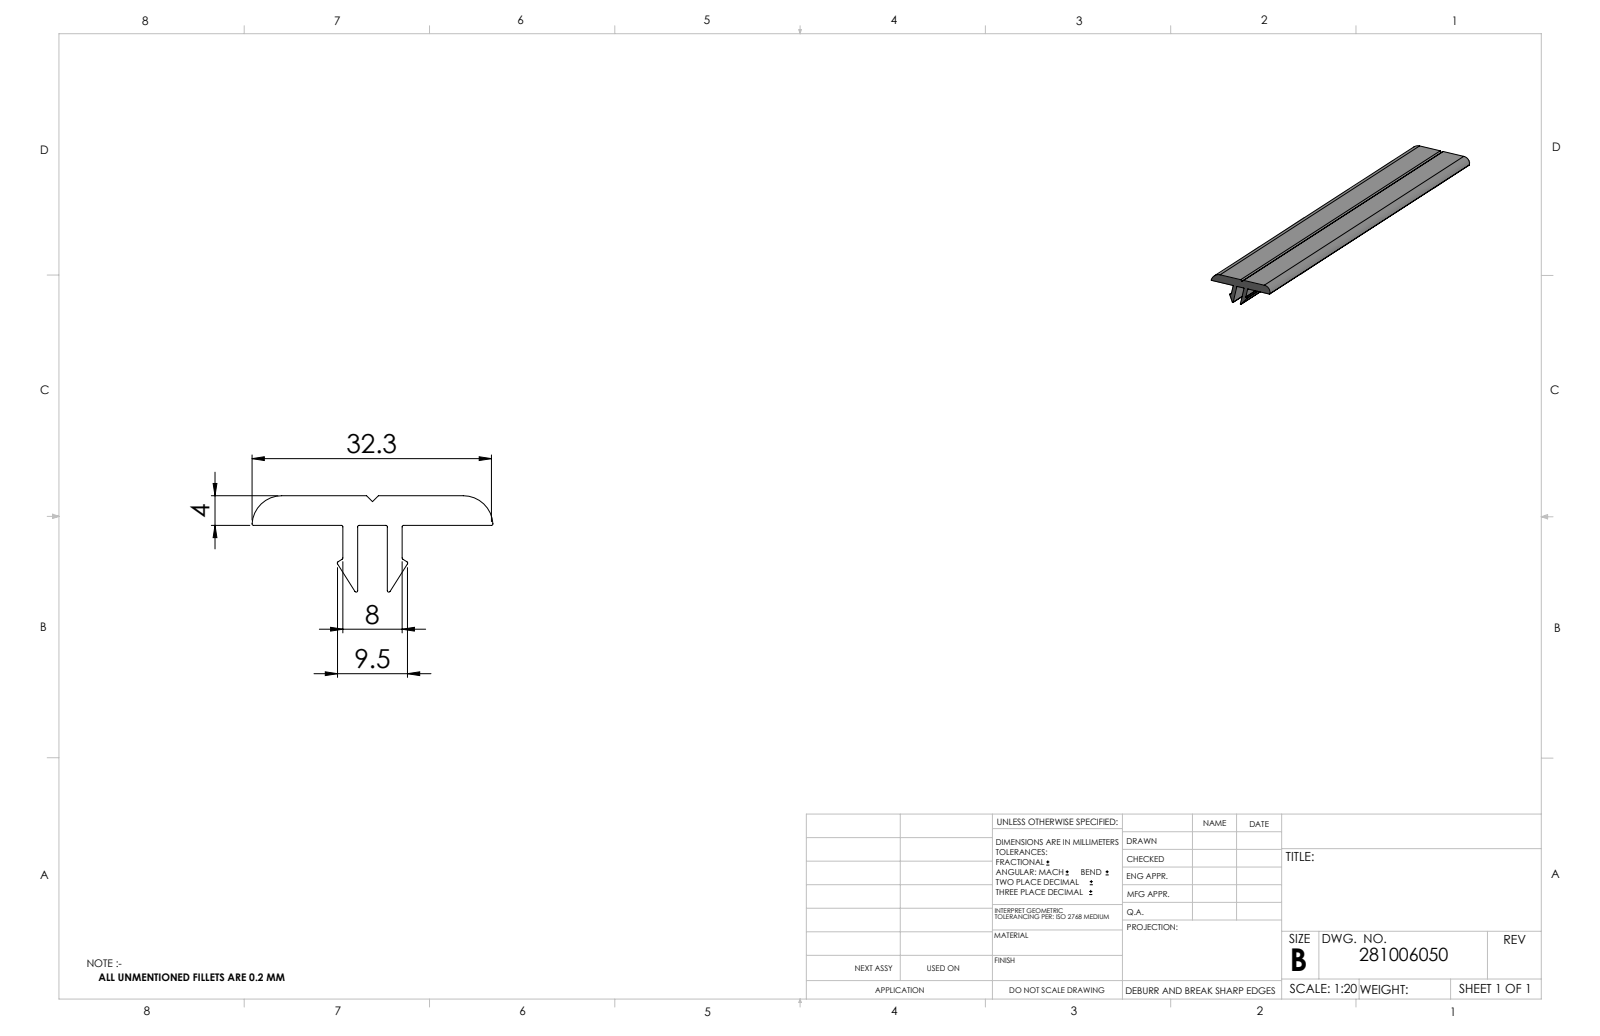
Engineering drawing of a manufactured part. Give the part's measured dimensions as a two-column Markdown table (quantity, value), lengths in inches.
| quantity | value |
| --- | --- |
| part name | 281006050_c_1 |
| STEP written by | SolidWorks 2014 (CONFIG_CONTROL_DESIGN) |
| units | inches |
| bodies | 1 solid, 33 faces (17 planar, 16 cylindrical, 0 other) |
| overall size | 78.74 × 1.28 × 0.512 |
| volume | 18.98 in³ |
| surface area | 323.8 in² |
| partial cylindrical surfaces (radius × count) | 0.008 × 12, 0.157 × 2 |
| main face-to-face distances | 0.157, 0.079, 0.236, 0.315, 78.74 |
